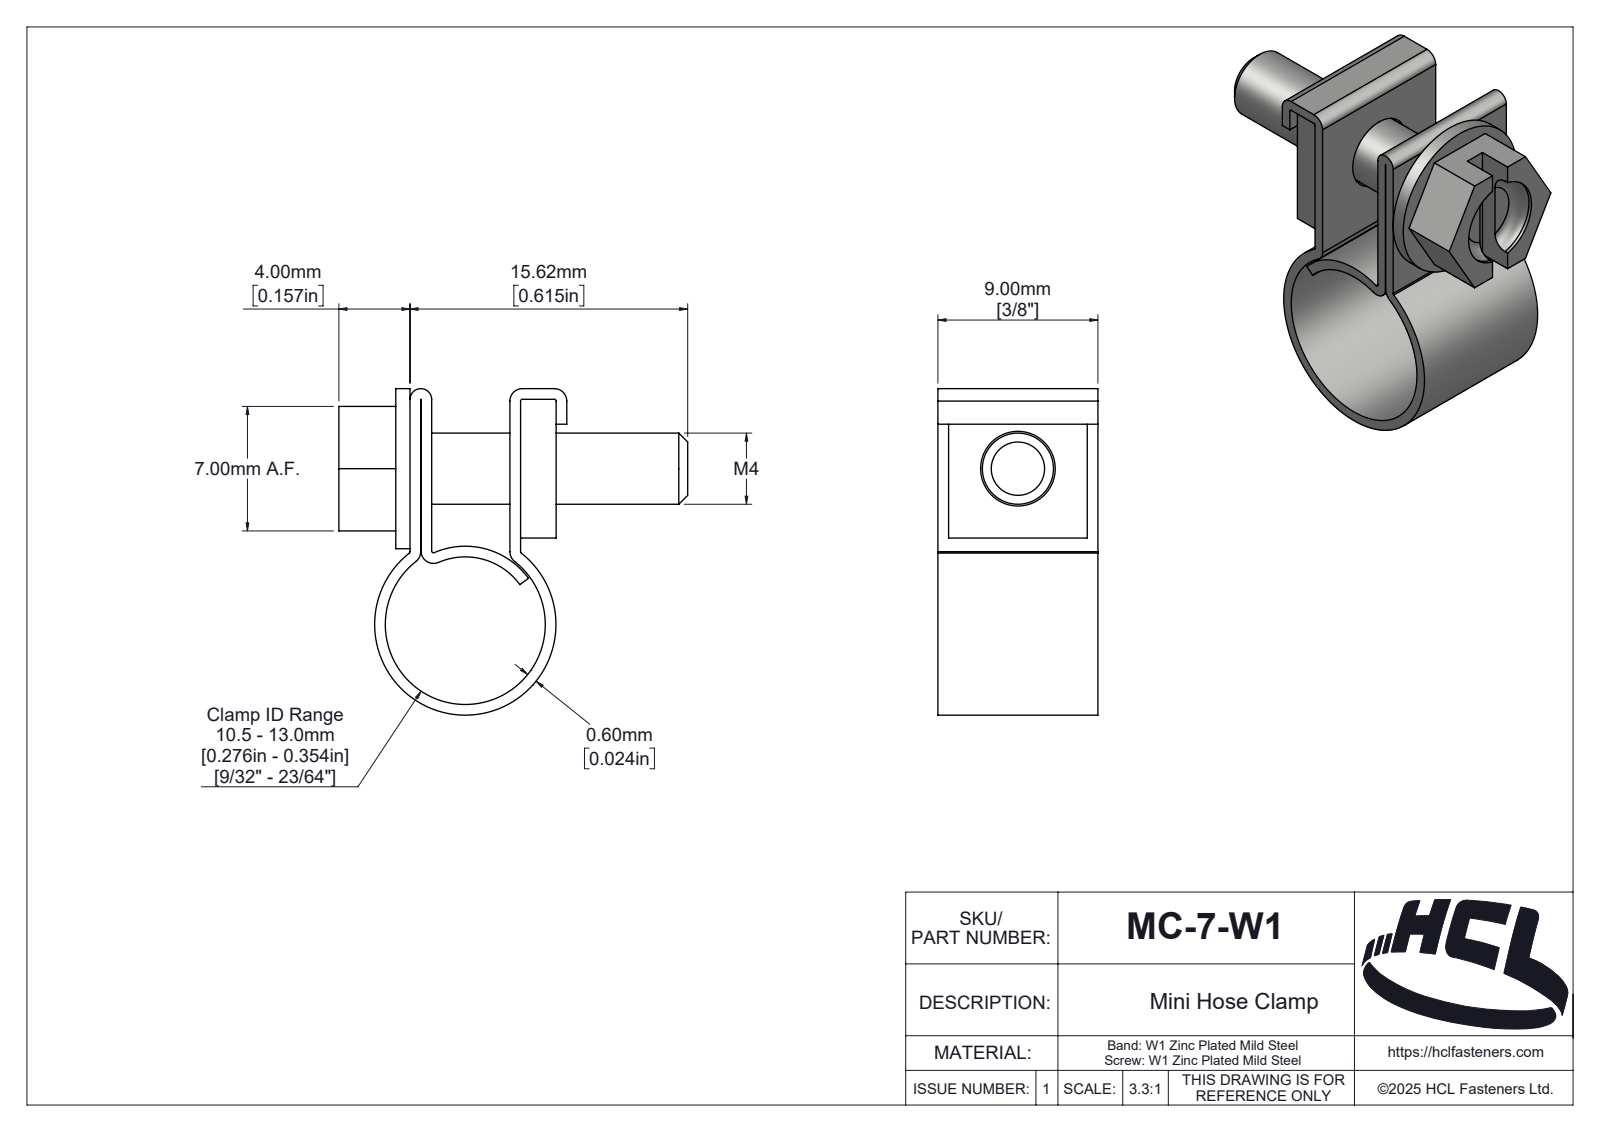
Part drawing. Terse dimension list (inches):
name: MC-8-W1
written by: SolidWorks 2025 (AUTOMOTIVE_DESIGN)
unit: in
bodies: 3 solids, 175 faces (38 planar, 84 cylindrical, 53 other)
size: 0.772 × 0.767 × 0.354
volume: 0.047 in³; area: 2.838 in²
holes: 1× ⌀0.165, 1× ⌀0.197, 1× ⌀0.394
bosses: 1× ⌀0.441, 1× ⌀0.354, 1× ⌀0.157
rounds: 5× R0.004, 5× R0.028, 1× R0.008, 1× R0.024, 1× R0.032, 1× R0.04, 1× R0.042, 1× R0.05
face distances: 0.024, 0.024, 0.197, 0.221, 0.245, 0.276, 0.079, 0.102, 0.324, 0.299
